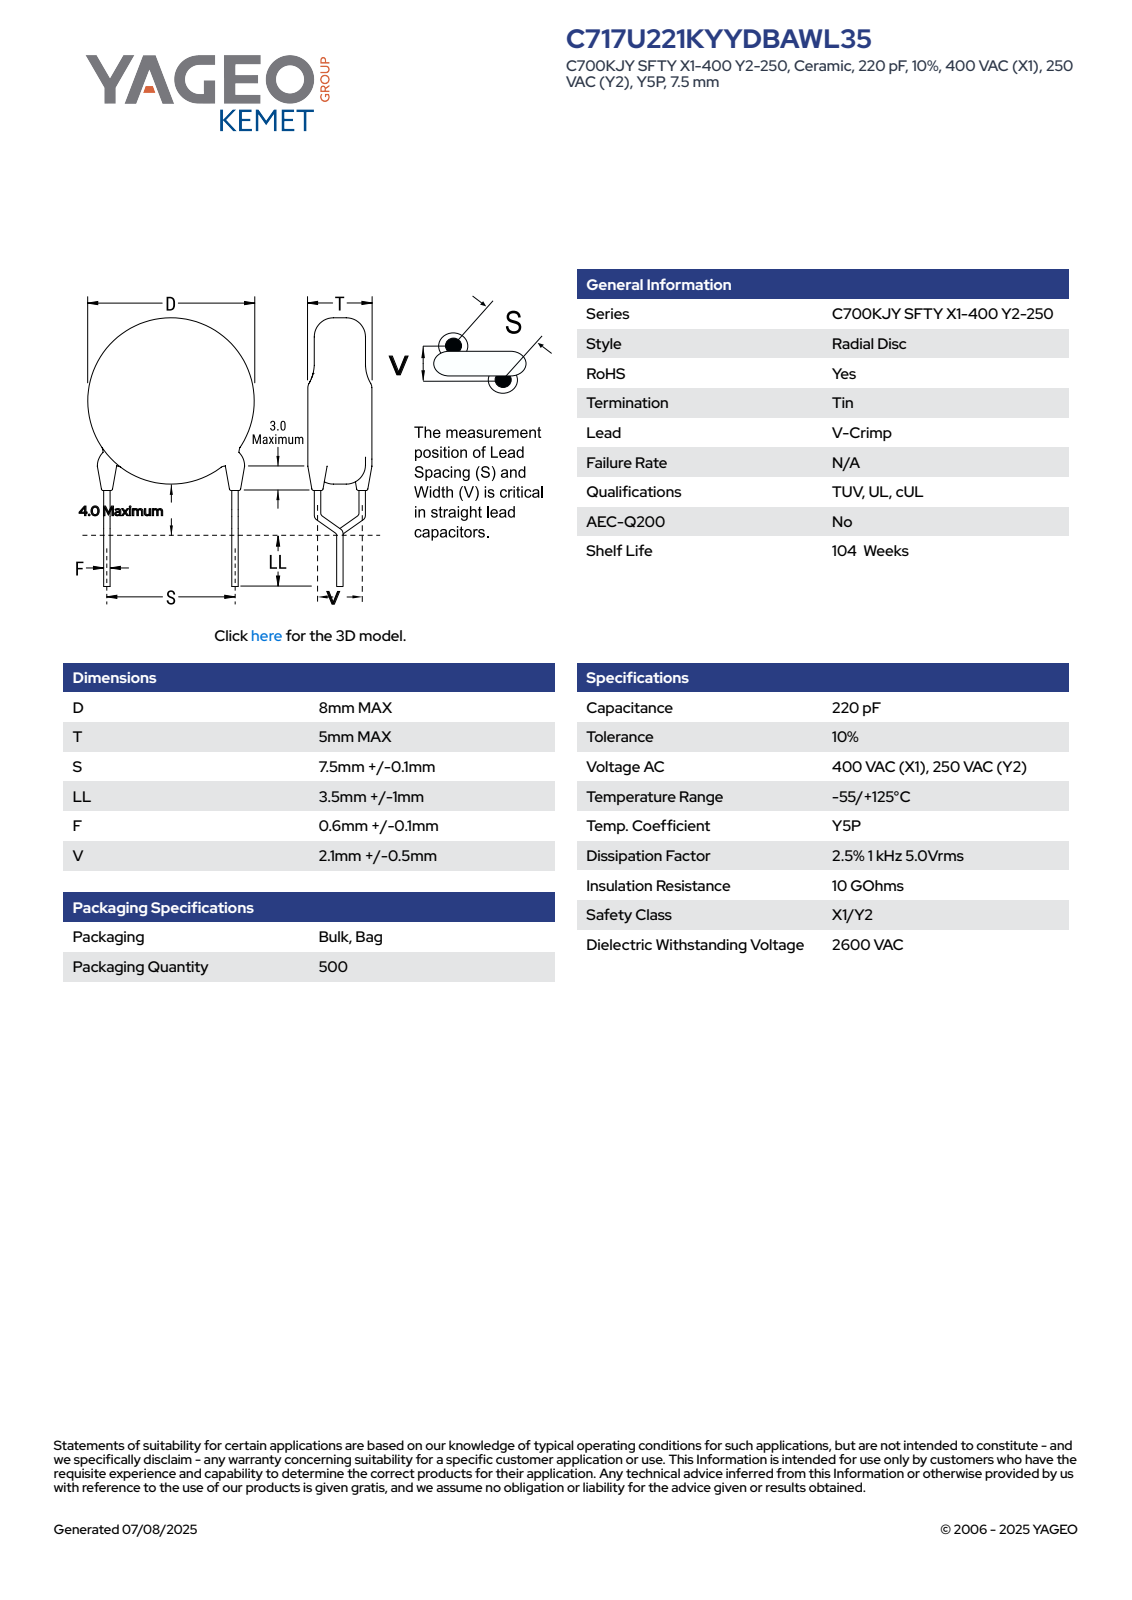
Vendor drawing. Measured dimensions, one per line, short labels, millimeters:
name: CCD_VC8X5_D8T5S7.5LL4.5F0.7V2.1
written by: SolidWorks 2021 (AUTOMOTIVE_DESIGN)
unit: mm
bodies: 4 solids, 89 faces (63 planar, 22 cylindrical, 4 other)
size: 12.5 × 8.7 × 5
volume: 249 mm³; area: 245 mm²
bosses: 6× ⌀0.7, 4× ⌀1.2, 1× ⌀8
face distances: 5, 4.5, 0.97, 9.13, 4.63, 8.16, 3.66, 0.36, 0.78, 0.35
